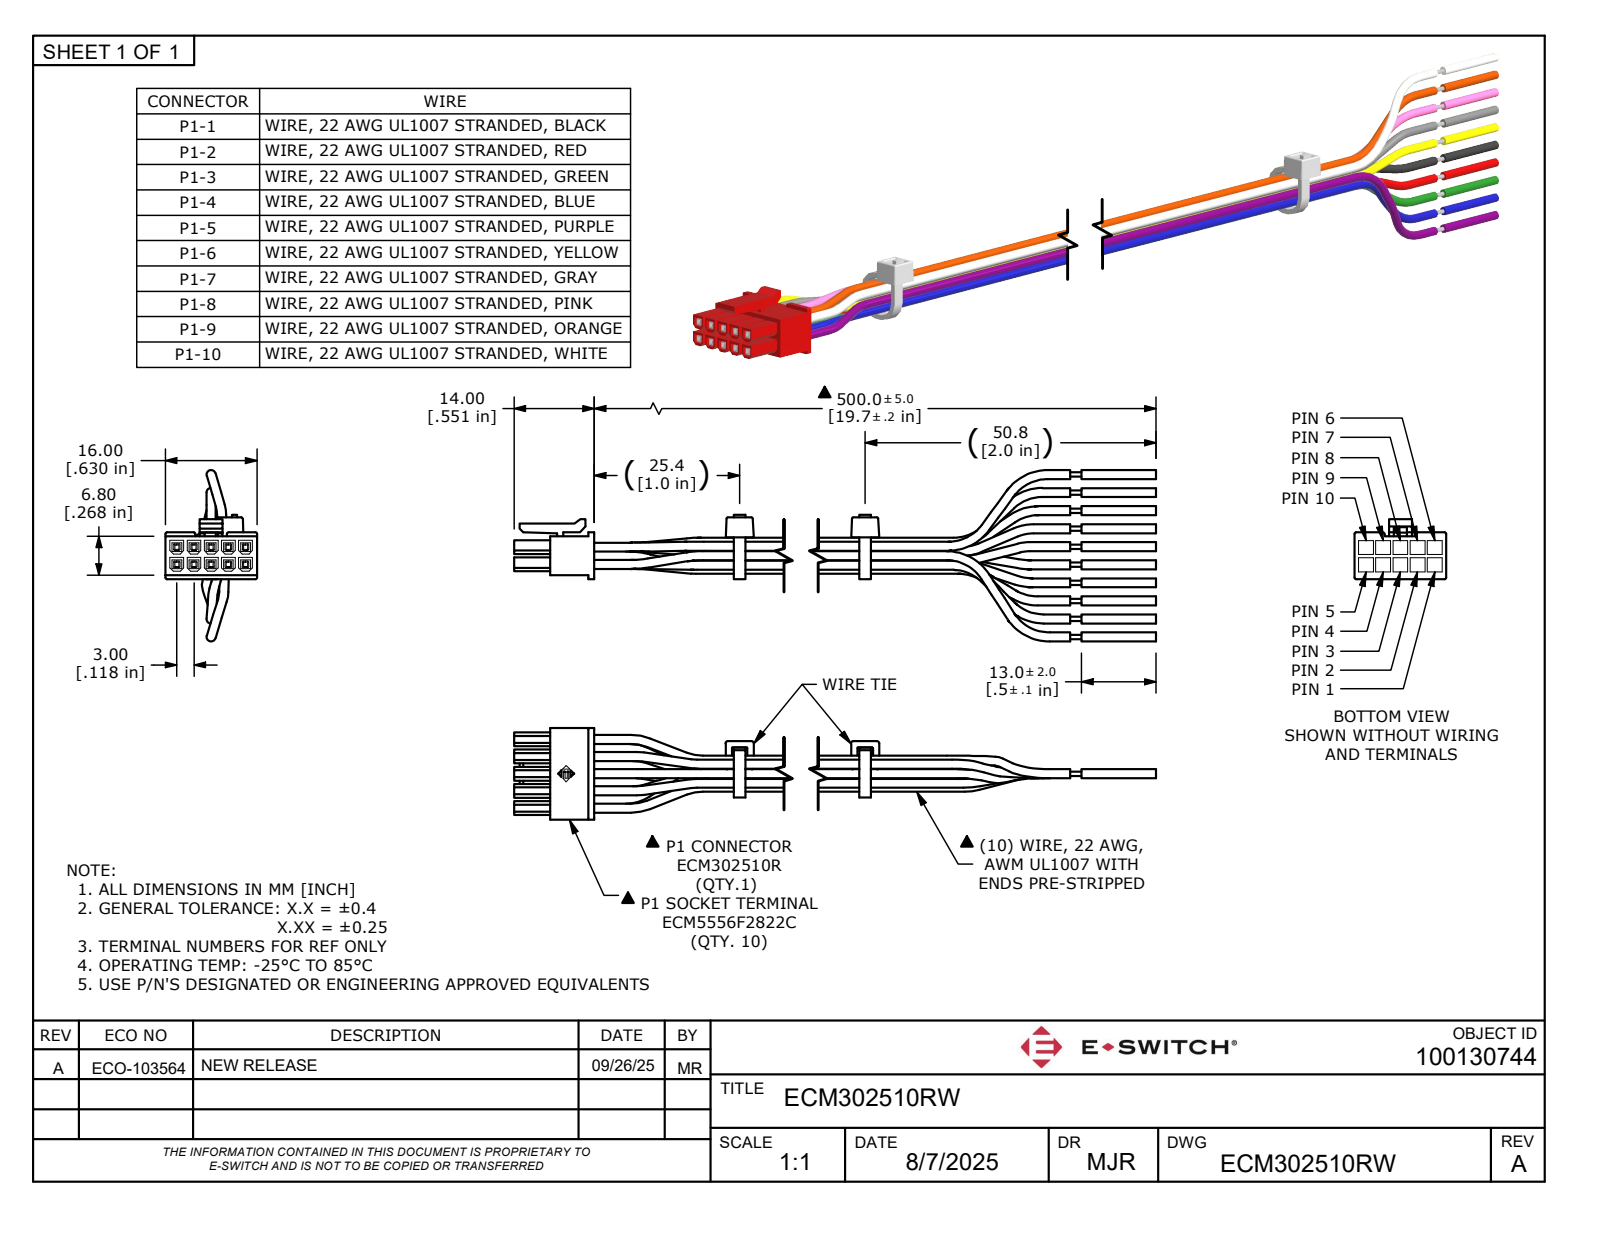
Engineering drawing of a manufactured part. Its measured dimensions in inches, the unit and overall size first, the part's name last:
Units: inches
Overall size (bounding box): 20.236 × 1.178 × 0.63
Round holes (diameter × count): ⌀0.016 ×4
Round bosses / shafts (diameter × count): ⌀0.062 ×54, ⌀0.03 ×10
Partial cylindrical surfaces — rounded edges, fillets, slot ends (radius × count): R0.008 ×152, R0.01 ×56, R0.016 ×50, R0.008 ×40, R0.012 ×16, R0.007 ×14, R0.006 ×12, R0.025 ×10
Main face-to-face distances: 0.118, 0.122, 0.077, 0.236, 0.24, 0.114, 0.094, 0.018, 0.059, 0.354
Hole centre spacings: 0.024, 0.118, 0.12
Volume: 0.659 in³ · Surface area: 44.47 in²
Bodies: 3 solids, 3123 faces (1558 planar, 1098 cylindrical, 467 other)
Part name (STEP PRODUCT): ECM302510RW
STEP written by: Autodesk Inventor 2022 (AUTOMOTIVE_DESIGN)
